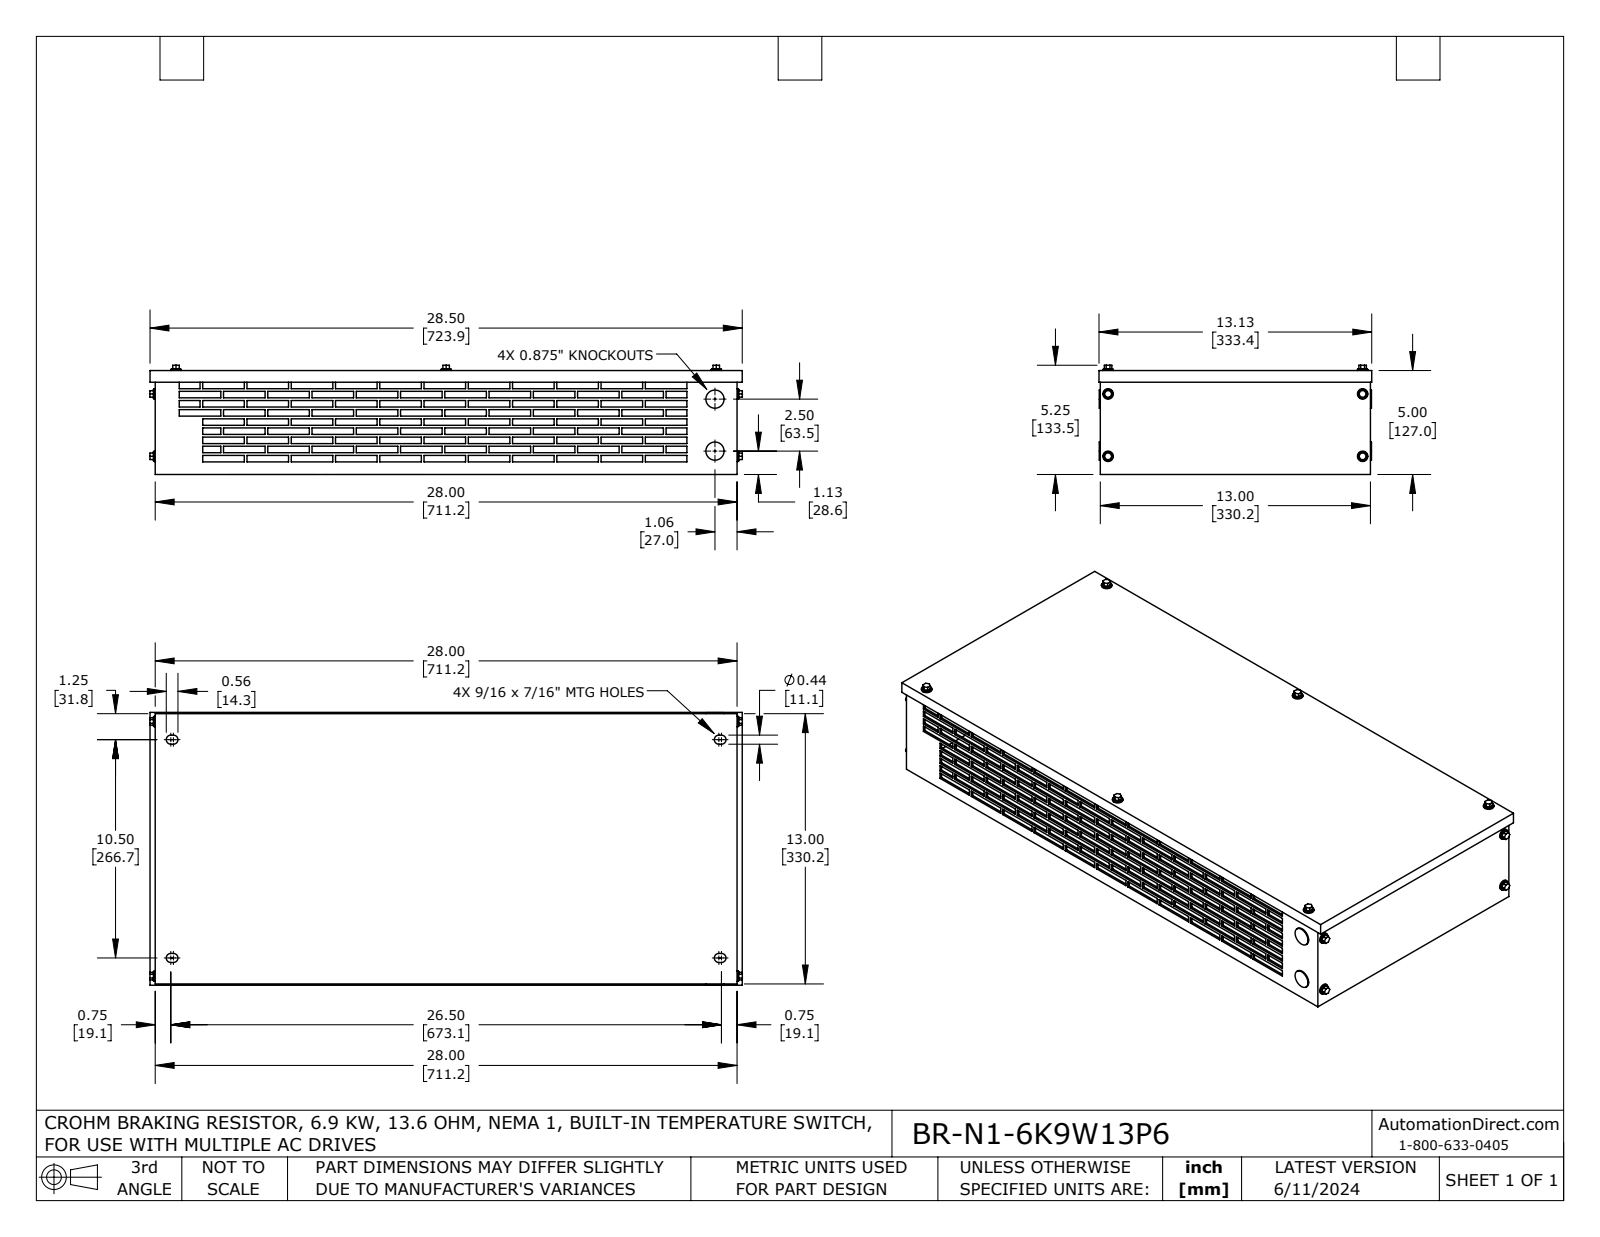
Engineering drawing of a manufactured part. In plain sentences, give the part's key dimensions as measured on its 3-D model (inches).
The part is named "BR-N1-6K9W13P6". Its 3-D file was written by "SolidWorks 2021 (AUTOMOTIVE_DESIGN)". It is 33 solids with 1120 faces: 1012 planar, 108 cylindrical and 0 other. Overall it measures 28.509 by 13.125 by 5.254 inches. Its volume is 101.7 cubic inches and its surface area 2 139 square inches. Round holes: 10 of diameter 0.25, 2 of diameter 0.75. Round bosses or shafts: 10 of diameter 0.5, 10 of diameter 0.437, 2 of diameter 0.875. Partial cylindrical surfaces (rounded edges, fillets, slot ends): 8 of radius 0.219. The main face-to-face distances are 0.1, 4.9, 5, 4.8, 12.9, 27.9, 13, 12.8, 28, 27.8. The hole center spacings are 12.25, 13, 17.862, 3, 12.611, 26, 28.741, 2.5.
